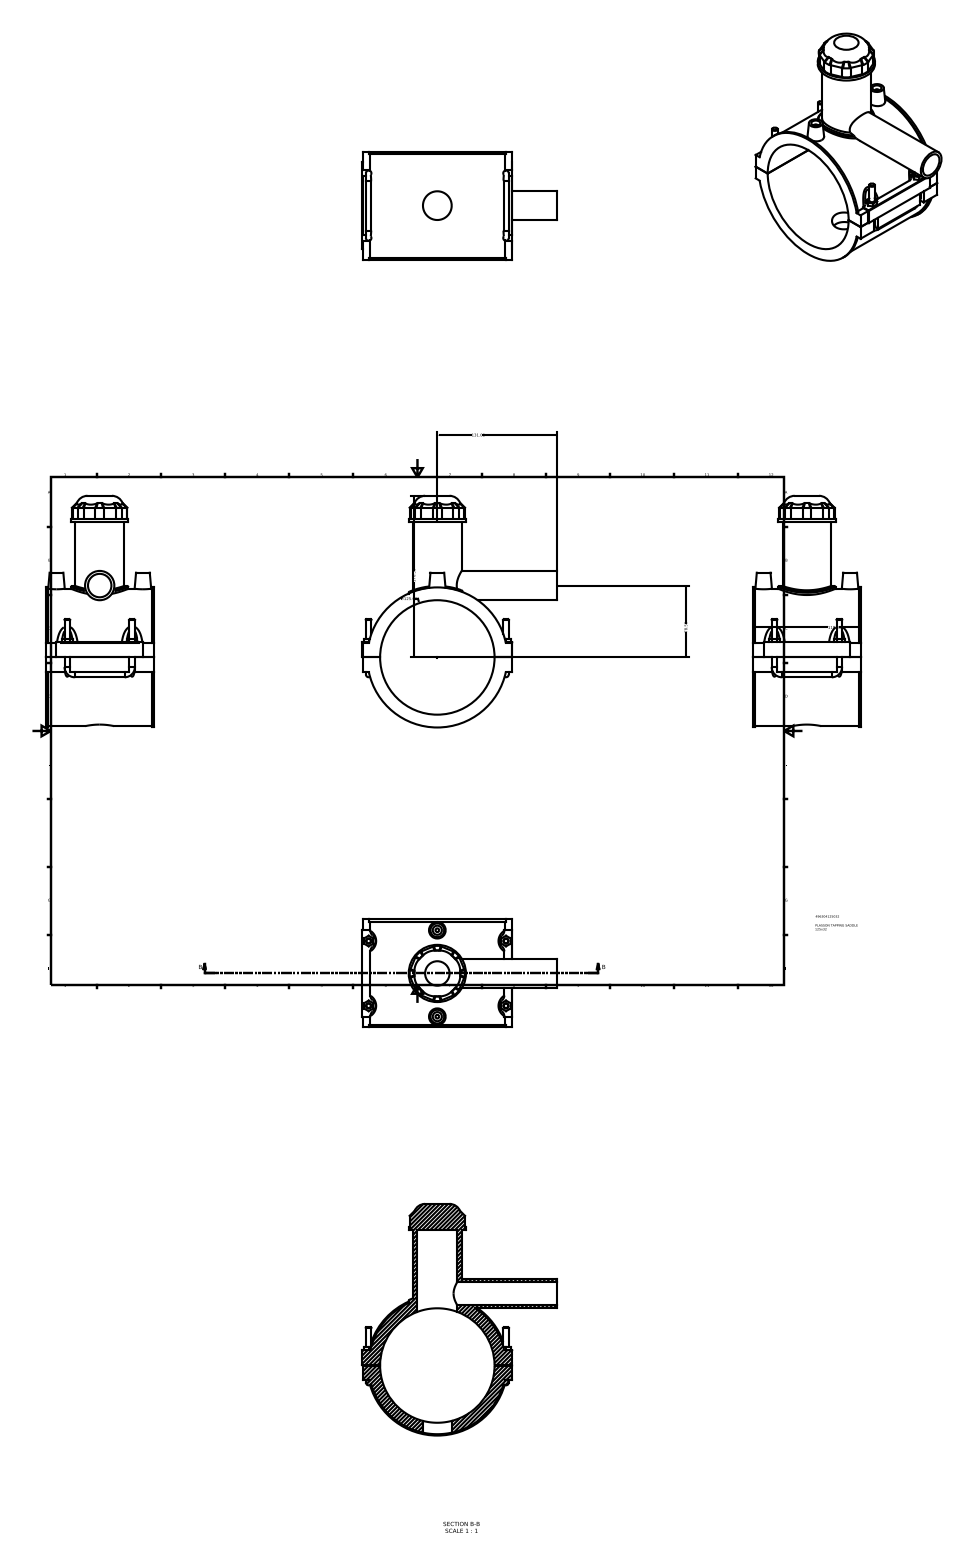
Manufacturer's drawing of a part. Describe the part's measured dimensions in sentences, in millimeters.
The part is named "496304125032". Its 3-D file was written by "Autodesk Inventor 2015 (AUTOMOTIVE_DESIGN)". It is 1 solid with 224 faces: 125 planar, 55 cylindrical and 44 other. Overall it measures 253 by 213 by 118 millimeters. Its volume is 823 484 cubic millimeters and its surface area 184 661 square millimeters. Round holes: 2 of diameter 10, 1 of diameter 25.6, 1 of diameter 31.36, 1 of diameter 43.75, 1 of diameter 125. Round bosses or shafts: 4 of diameter 6, 2 of diameter 4, 1 of diameter 153, 1 of diameter 150, 1 of diameter 62.5, 1 of diameter 53.12, 1 of diameter 32. Partial cylindrical surfaces (rounded edges, fillets, slot ends): 8 of radius 12.5, 6 of radius 3, 4 of radius 7.5, 1 of radius 0.5, 1 of radius 78. The main face-to-face distances are 118, 1, 163, 148.05, 147.95, 162, 15.57, 15.67, 163.62, 32.25. The hole center spacings are 47.2, 94.4.
